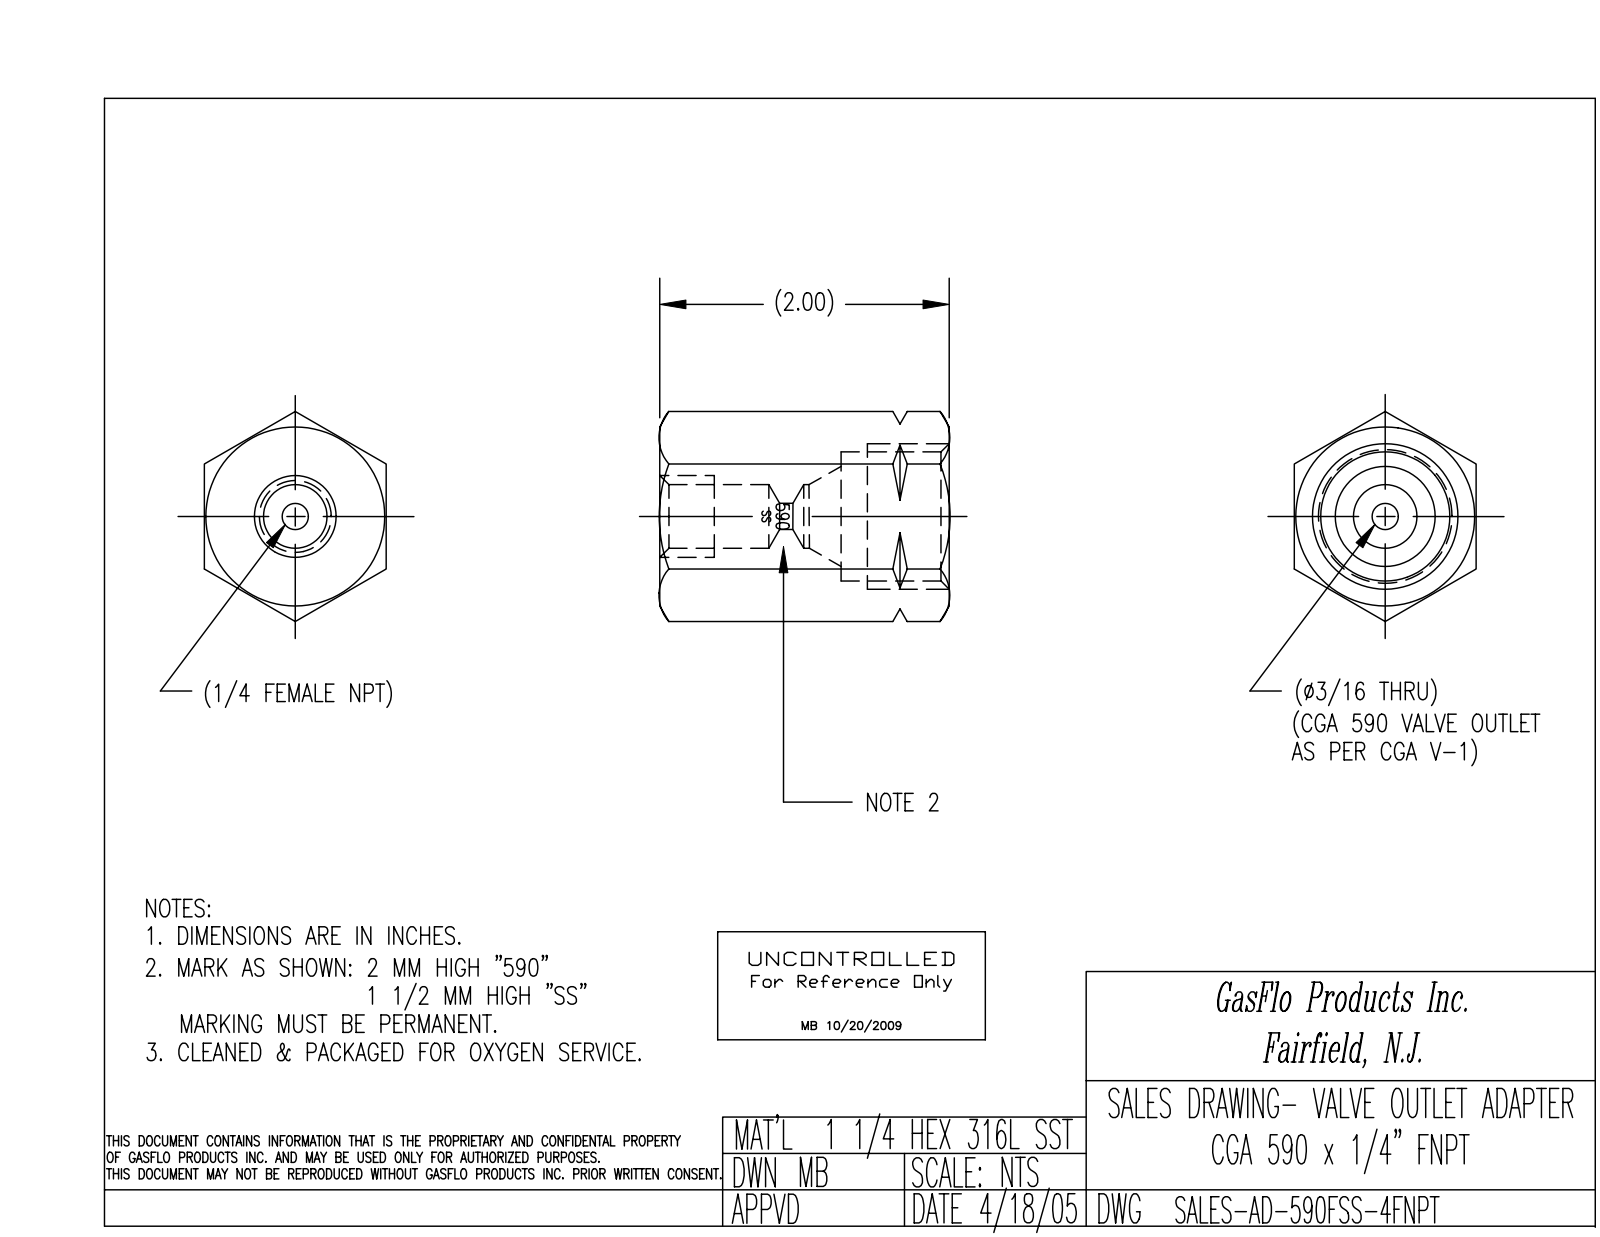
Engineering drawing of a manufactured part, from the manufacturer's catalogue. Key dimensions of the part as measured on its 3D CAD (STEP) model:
Part name (STEP PRODUCT): AD-590FSS-4FNPT
STEP written by: SolidWorks 2018 (CONFIG_CONTROL_DESIGN)
Units: inches
Bodies: 1 solid, 89 faces (16 planar, 25 cylindrical, 48 other)
Overall size (bounding box): 2 × 1.443 × 1.25
Volume: 2.028 in³ · Surface area: 16.29 in²
Round holes (diameter × count): ⌀0.187 ×1, ⌀0.422 ×1, ⌀0.422 ×1, ⌀0.892 ×1
Main face-to-face distances: 1.25, 1.25, 2, 1.313, 0.687
